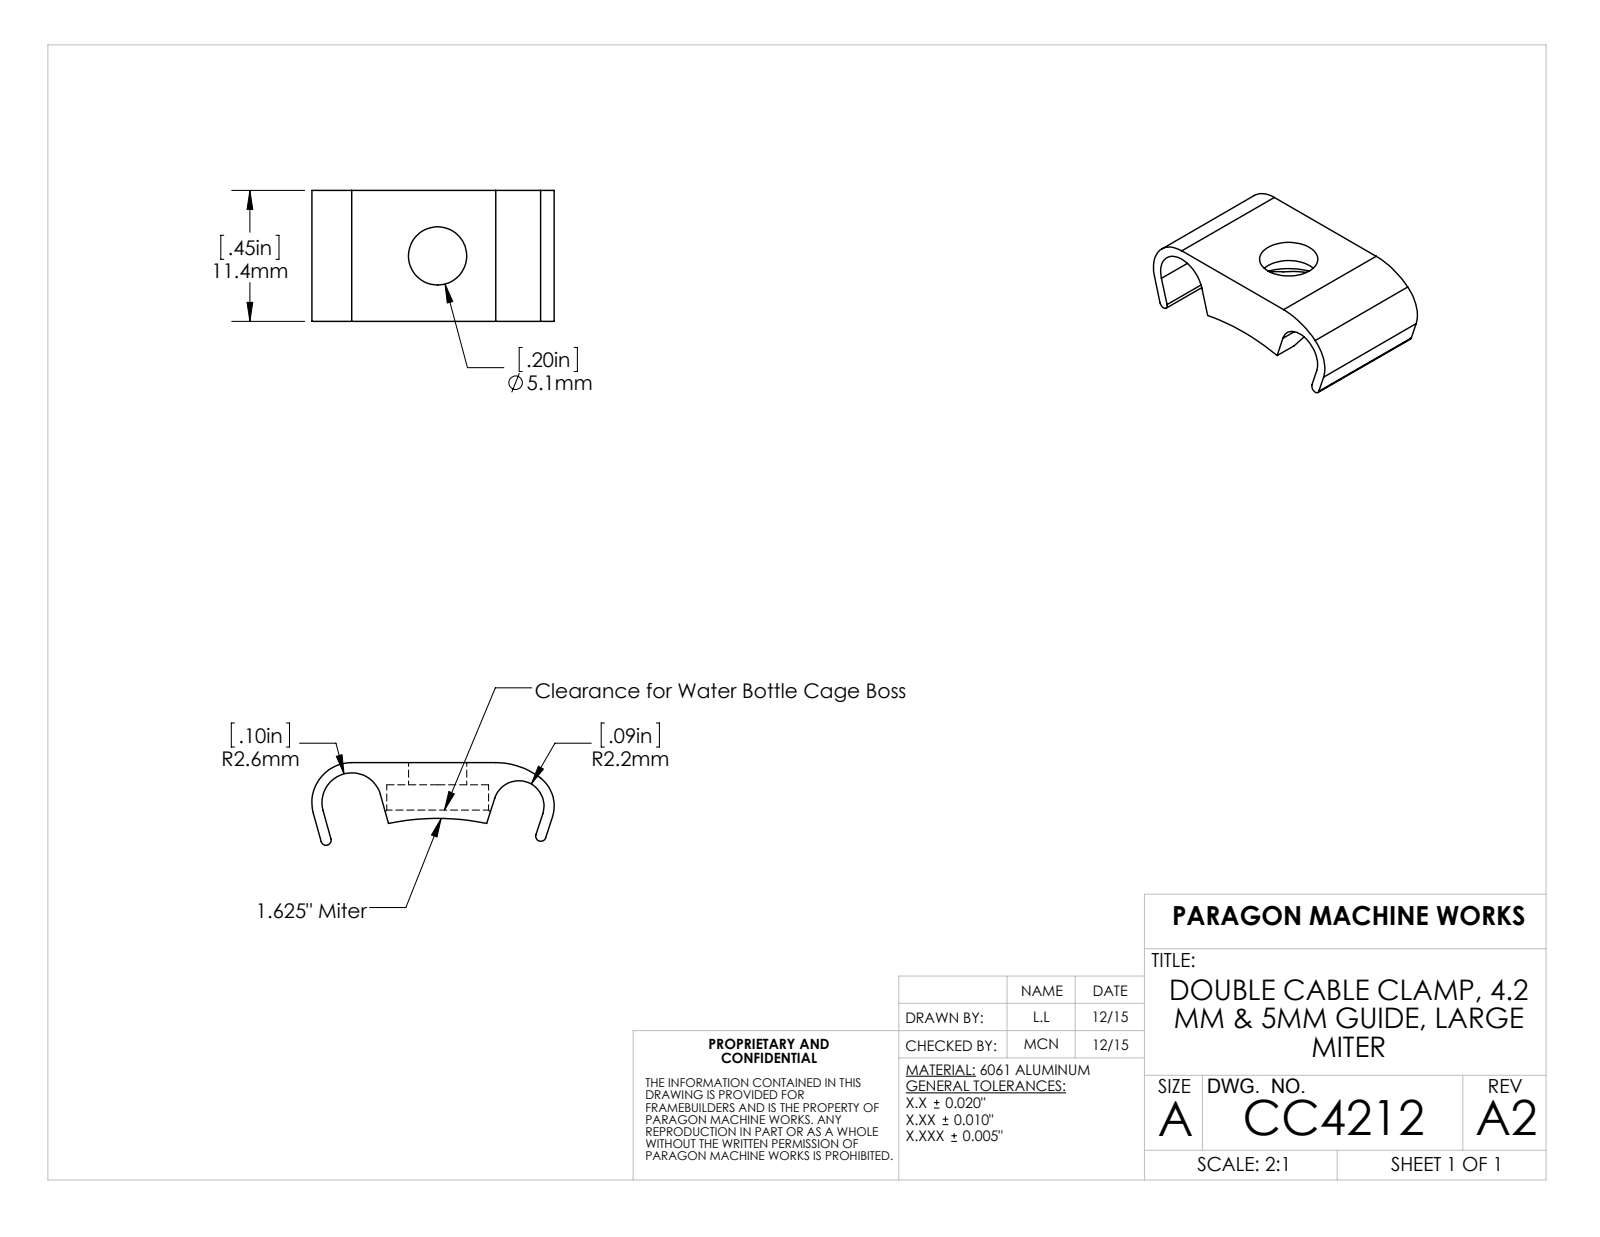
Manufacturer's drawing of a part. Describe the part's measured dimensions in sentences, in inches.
The part is named "CC4212". Its 3-D file was written by "SolidWorks 2015 (AUTOMOTIVE_DESIGN)". It is 1 solid with 28 faces: 10 planar, 16 cylindrical and 2 other. Overall it measures 0.833 by 0.45 by 0.284 inches. Its volume is 0.035 cubic inches and its surface area 1.494 square inches. Round holes: 1 of diameter 0.2, 1 of diameter 0.35. Partial cylindrical surfaces (rounded edges, fillets, slot ends): 2 of radius 0.018, 1 of radius 0.087, 1 of radius 0.102, 1 of radius 0.122, 1 of radius 0.137, 1 of radius 0.25, 1 of radius 0.823. The main face-to-face distances are 0.45, 0.035, 0.076, 0.239, 0.204, 0.173, 0.208.
